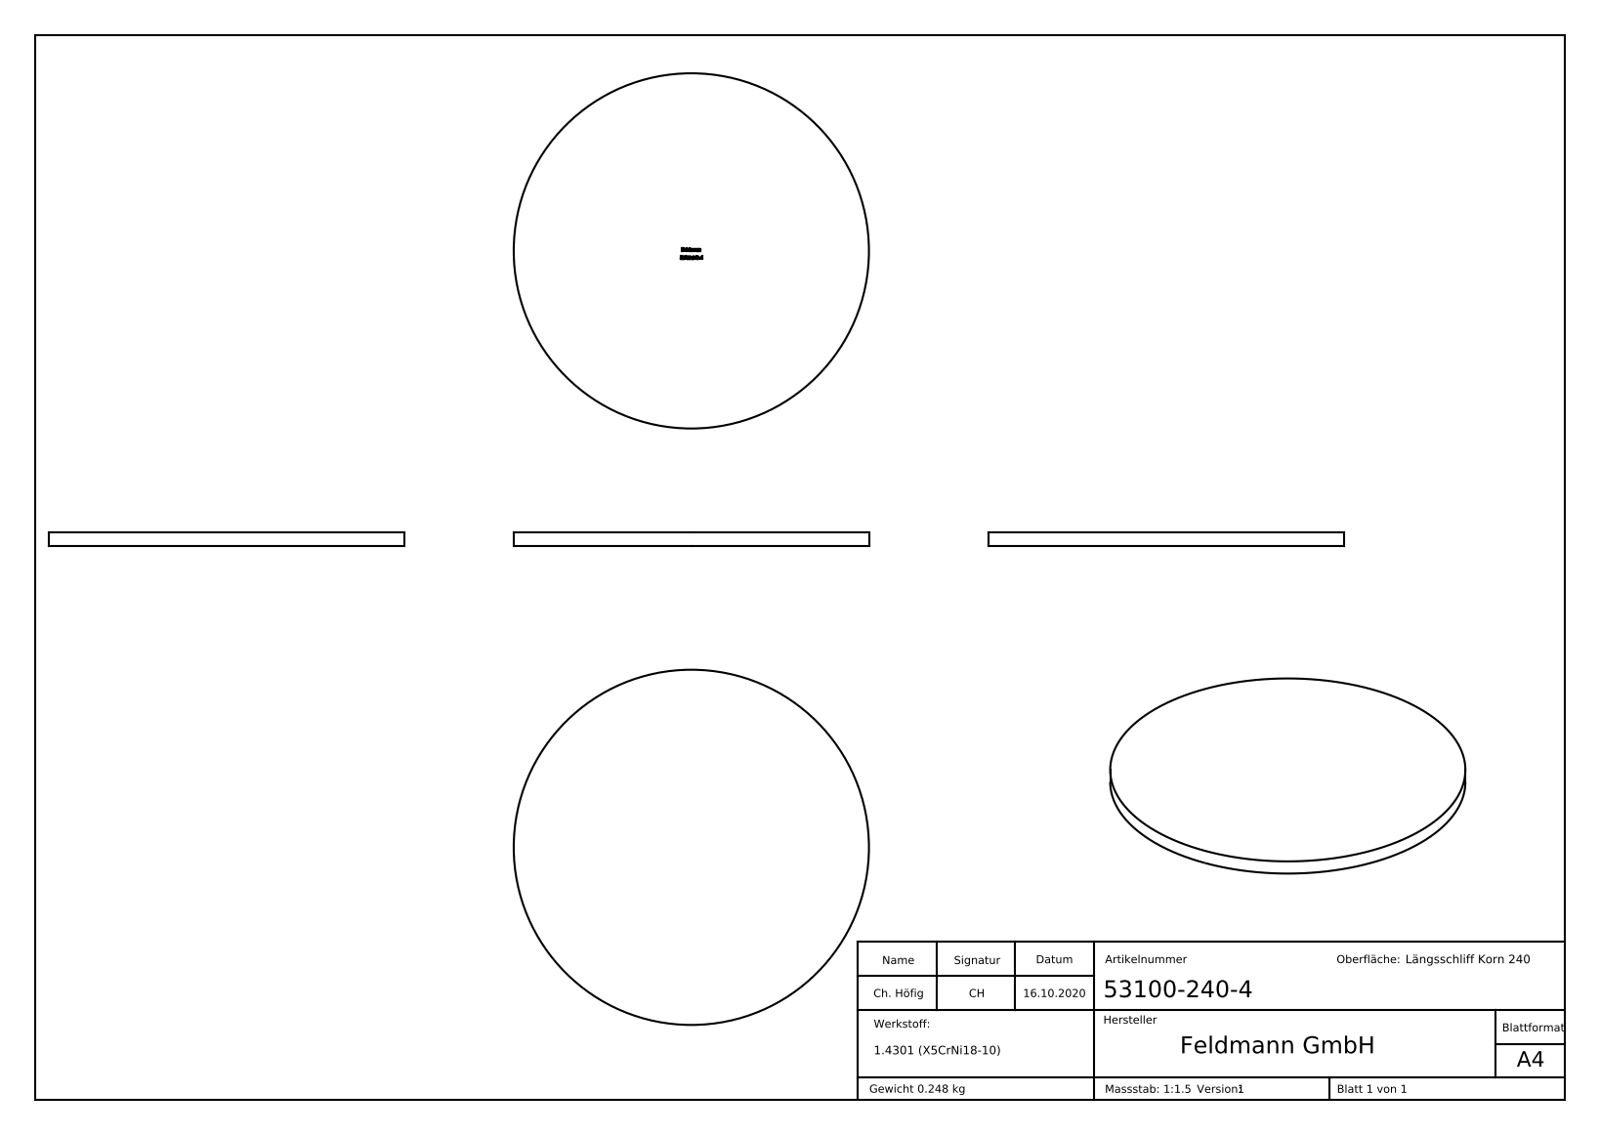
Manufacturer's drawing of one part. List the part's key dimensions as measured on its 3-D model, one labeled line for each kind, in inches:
Part name (STEP PRODUCT): 53100-240-4
STEP written by: SolidWorks 2018 (CONFIG_CONTROL_DESIGN)
Units: inches
Bodies: 1 solid, 243 faces (138 planar, 2 cylindrical, 103 other)
Overall size (bounding box): 3.937 × 3.937 × 0.157
Volume: 1.917 in³ · Surface area: 26.31 in²
Round bosses / shafts (diameter × count): ⌀3.937 ×1
Main face-to-face distances: 0.157, 0.154, 0.033, 0.103, 0.03, 0.07, 0.037, 0.109, 0.04, 0.119
